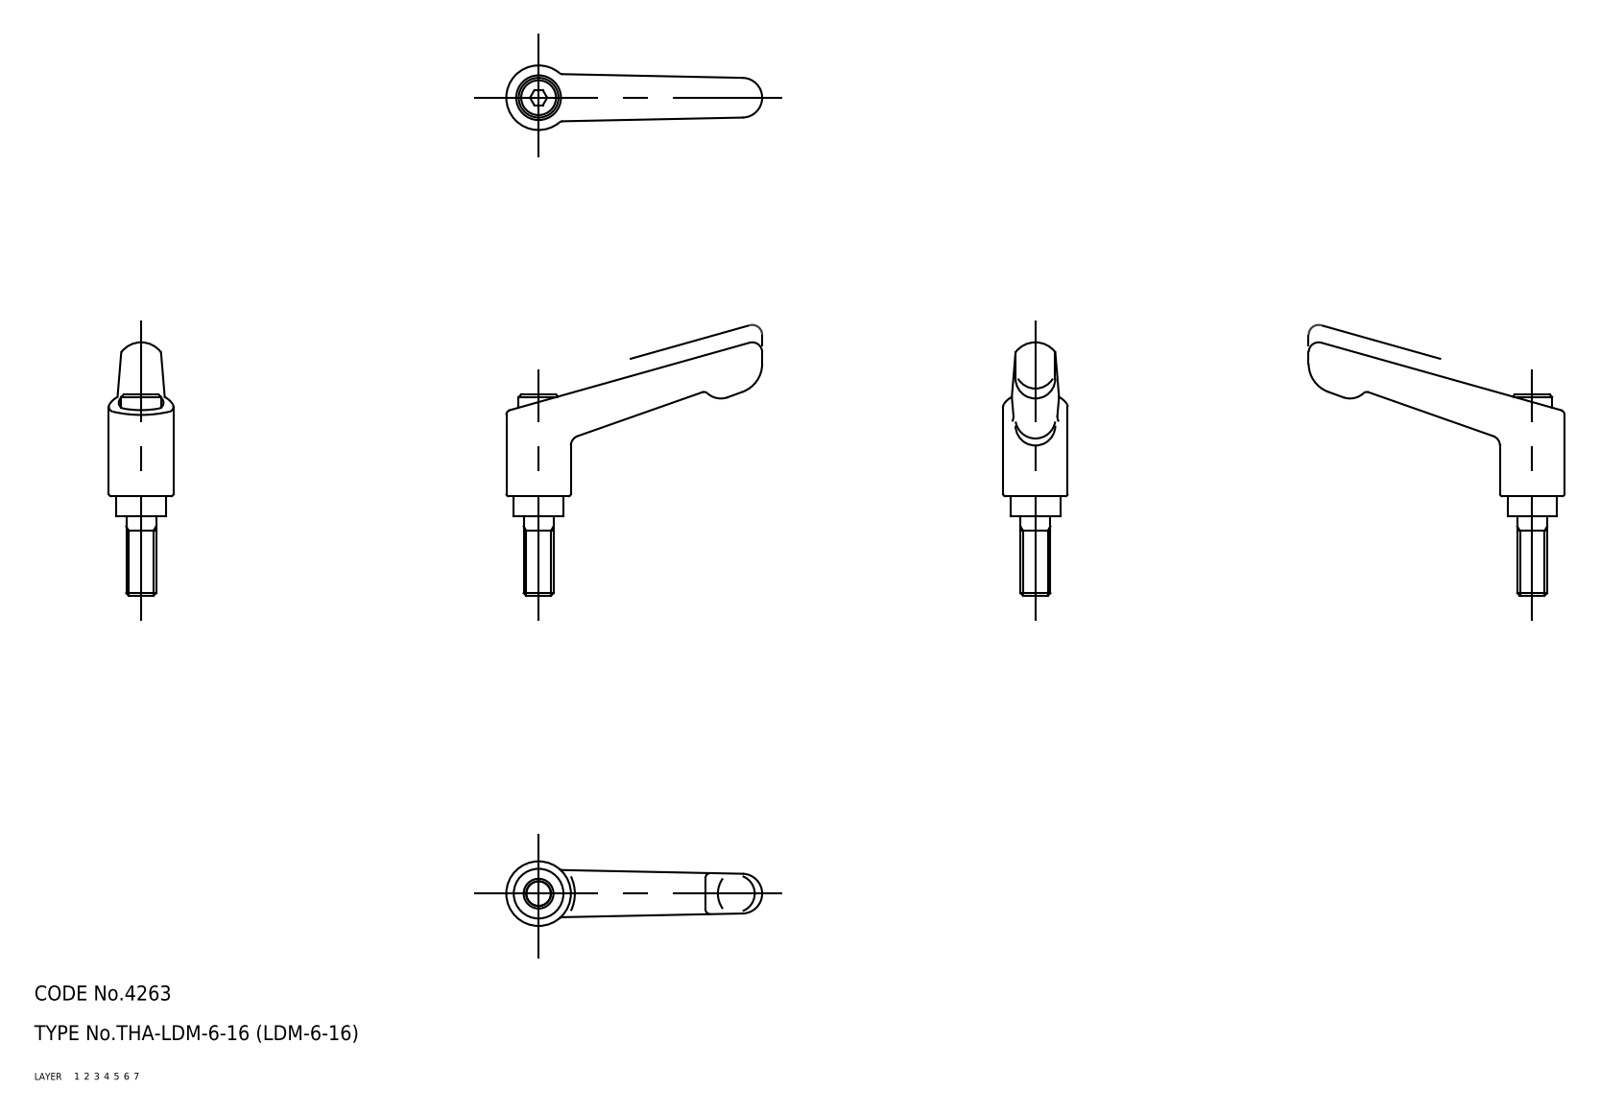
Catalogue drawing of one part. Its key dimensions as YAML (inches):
part_name: "sleeve; screw; handle; LDM_6_16_13074_36"
step_written_by: "CADfix (AUTOMOTIVE_DESIGN)"
units: inches
bodies: {solids: 3, faces: 70, planar: 0, cylindrical: 0, other: 70}
overall_size: [2.028, 2.008, 0.512]
volume: 0.341
surface_area: 5.915
